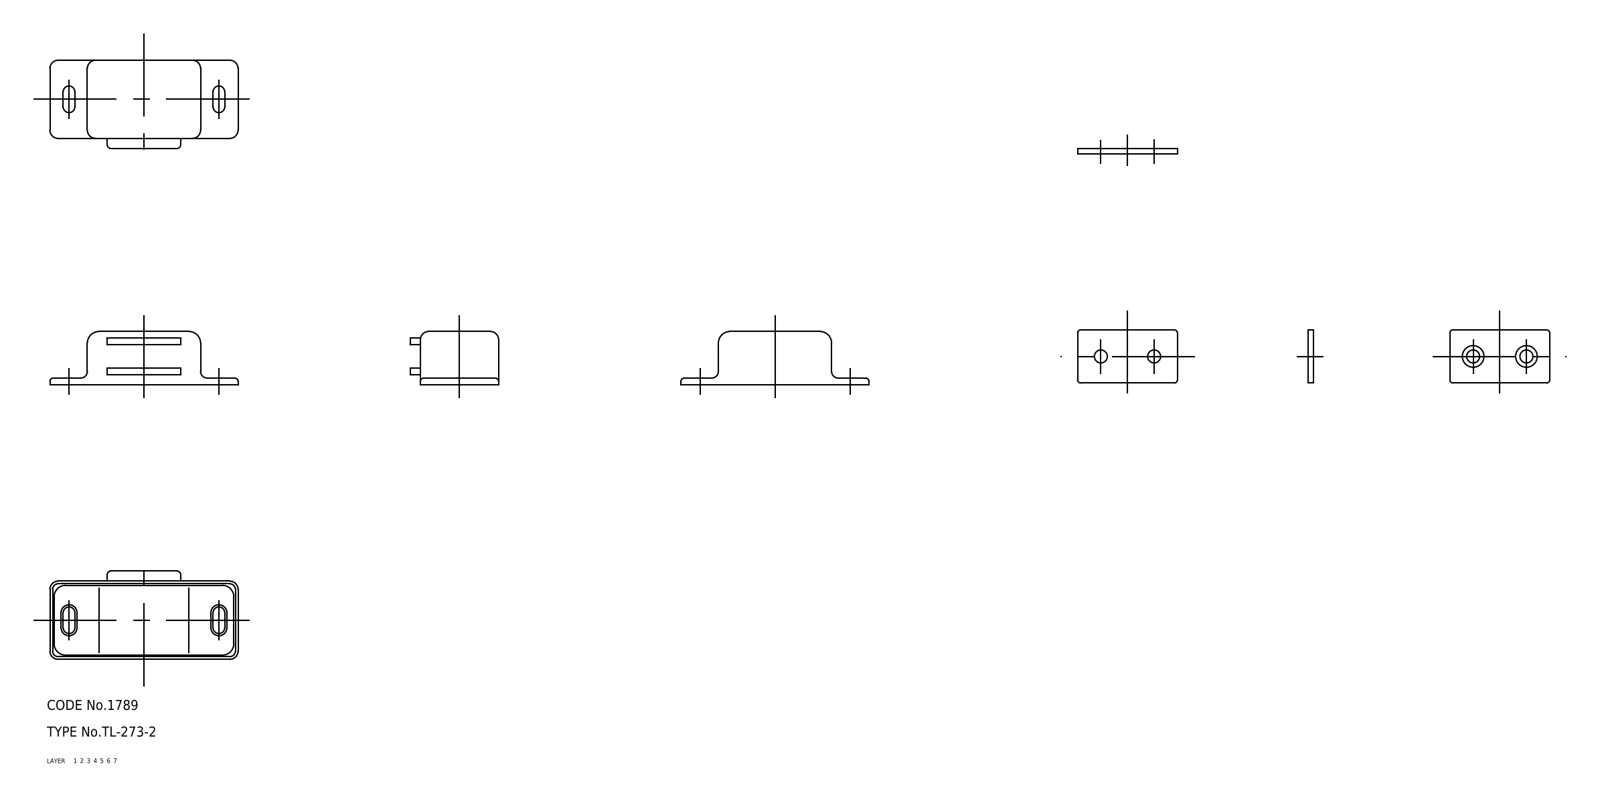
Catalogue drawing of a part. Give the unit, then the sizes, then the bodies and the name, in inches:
Units: inches
Overall size (bounding box): 2.224 × 2.15 × 0.65
Volume: 0.354 in³ · Surface area: 17.73 in²
Bodies: 5 solids, 175 faces (0 planar, 0 cylindrical, 175 other)
Part name (STEP PRODUCT): attachment; keeper; housing; base (+1 more)
STEP written by: CADfix (AUTOMOTIVE_DESIGN)
